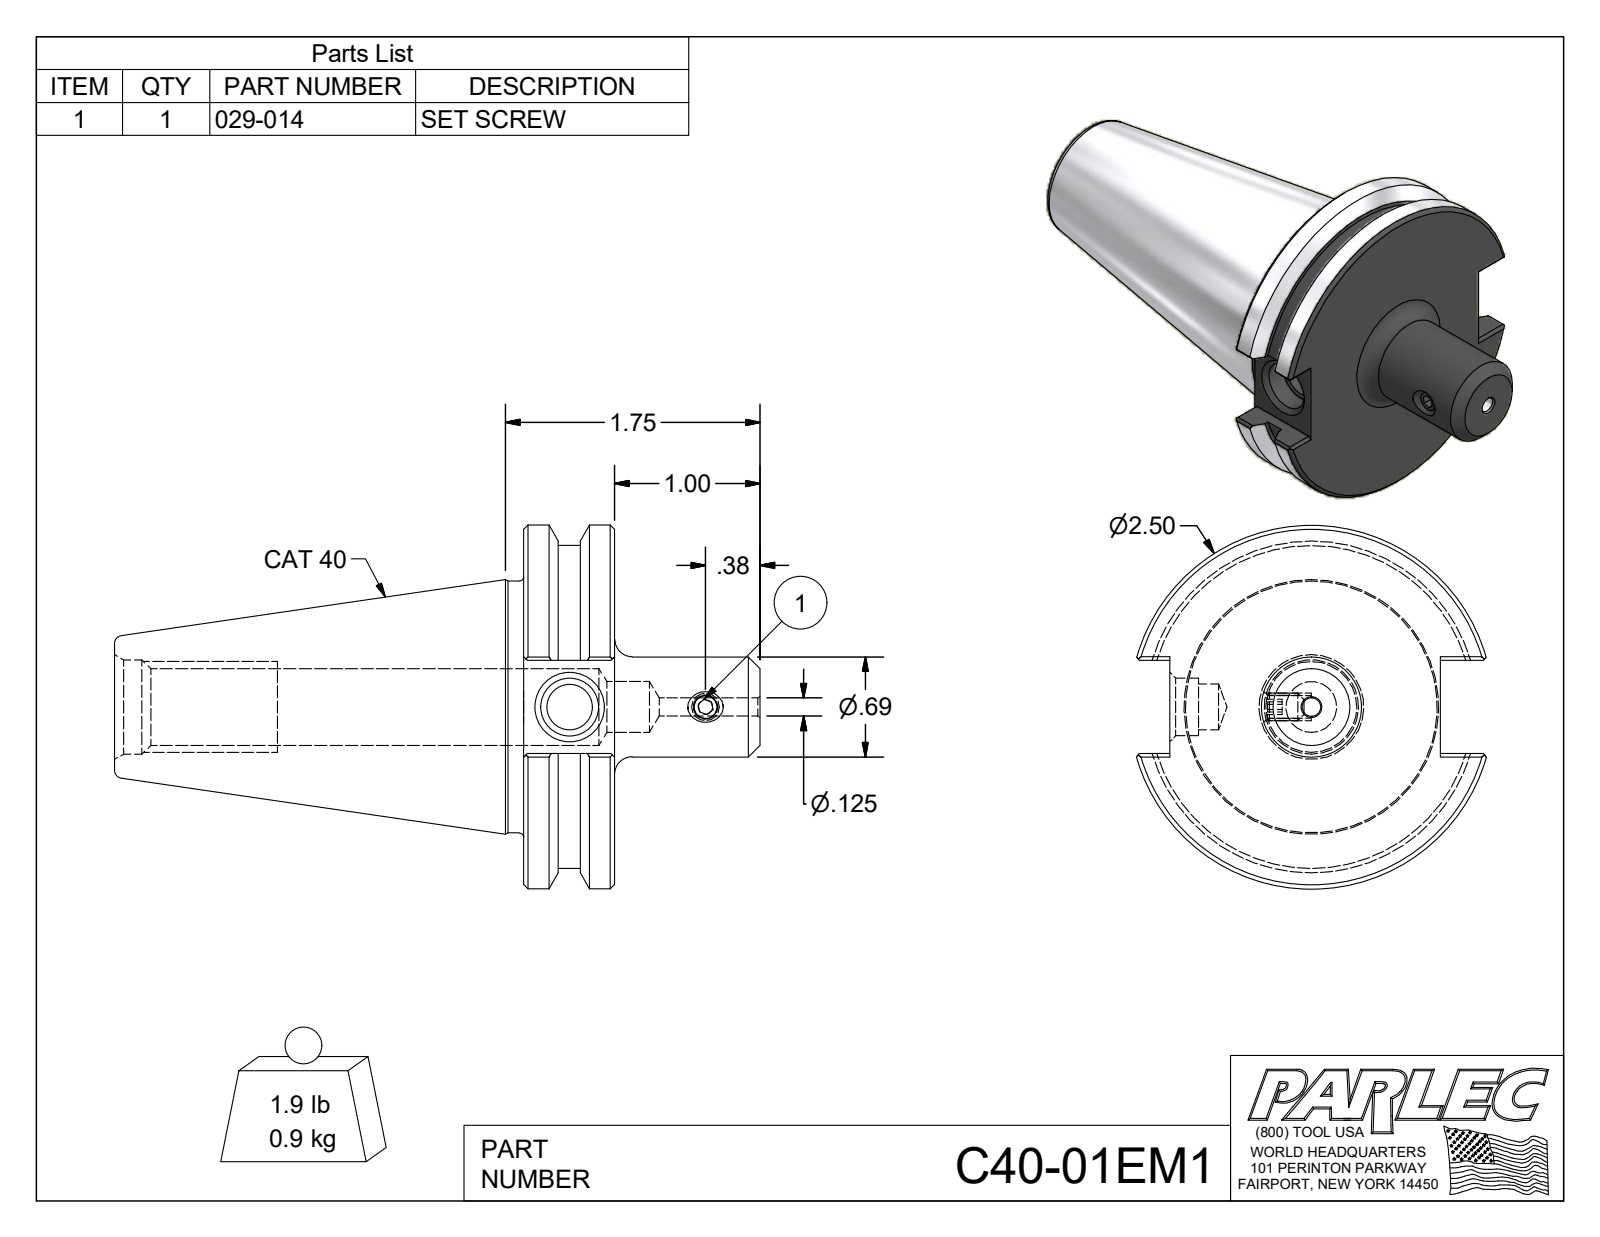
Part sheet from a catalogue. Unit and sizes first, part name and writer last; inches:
Units: inches
Overall size (bounding box): 4.438 × 2.5 × 2.403
Round holes (diameter × count): ⌀0.156 ×1, ⌀0.312 ×1, ⌀0.315 ×1, ⌀0.35 ×1, ⌀0.396 ×1, ⌀0.527 ×1, ⌀0.648 ×1
Round bosses / shafts (diameter × count): ⌀2.5 ×1, ⌀2.219 ×1, ⌀1.73 ×1, ⌀0.687 ×1, ⌀0.19 ×1
Main face-to-face distances: 0.625, 0.64, 1.86, 2.813, 3.437, 3.201, 0.389, 0.236, 3.05, 0.238
Hole centre spacings: 0.935
Volume: 6.426 in³ · Surface area: 34.7 in²
Bodies: 2 solids, 80 faces (40 planar, 16 cylindrical, 24 other)
Part name (STEP PRODUCT): C40-01EM1; C40-01EM1-1; 029-014
STEP written by: Autodesk Inventor 2012 (AUTOMOTIVE_DESIGN)
